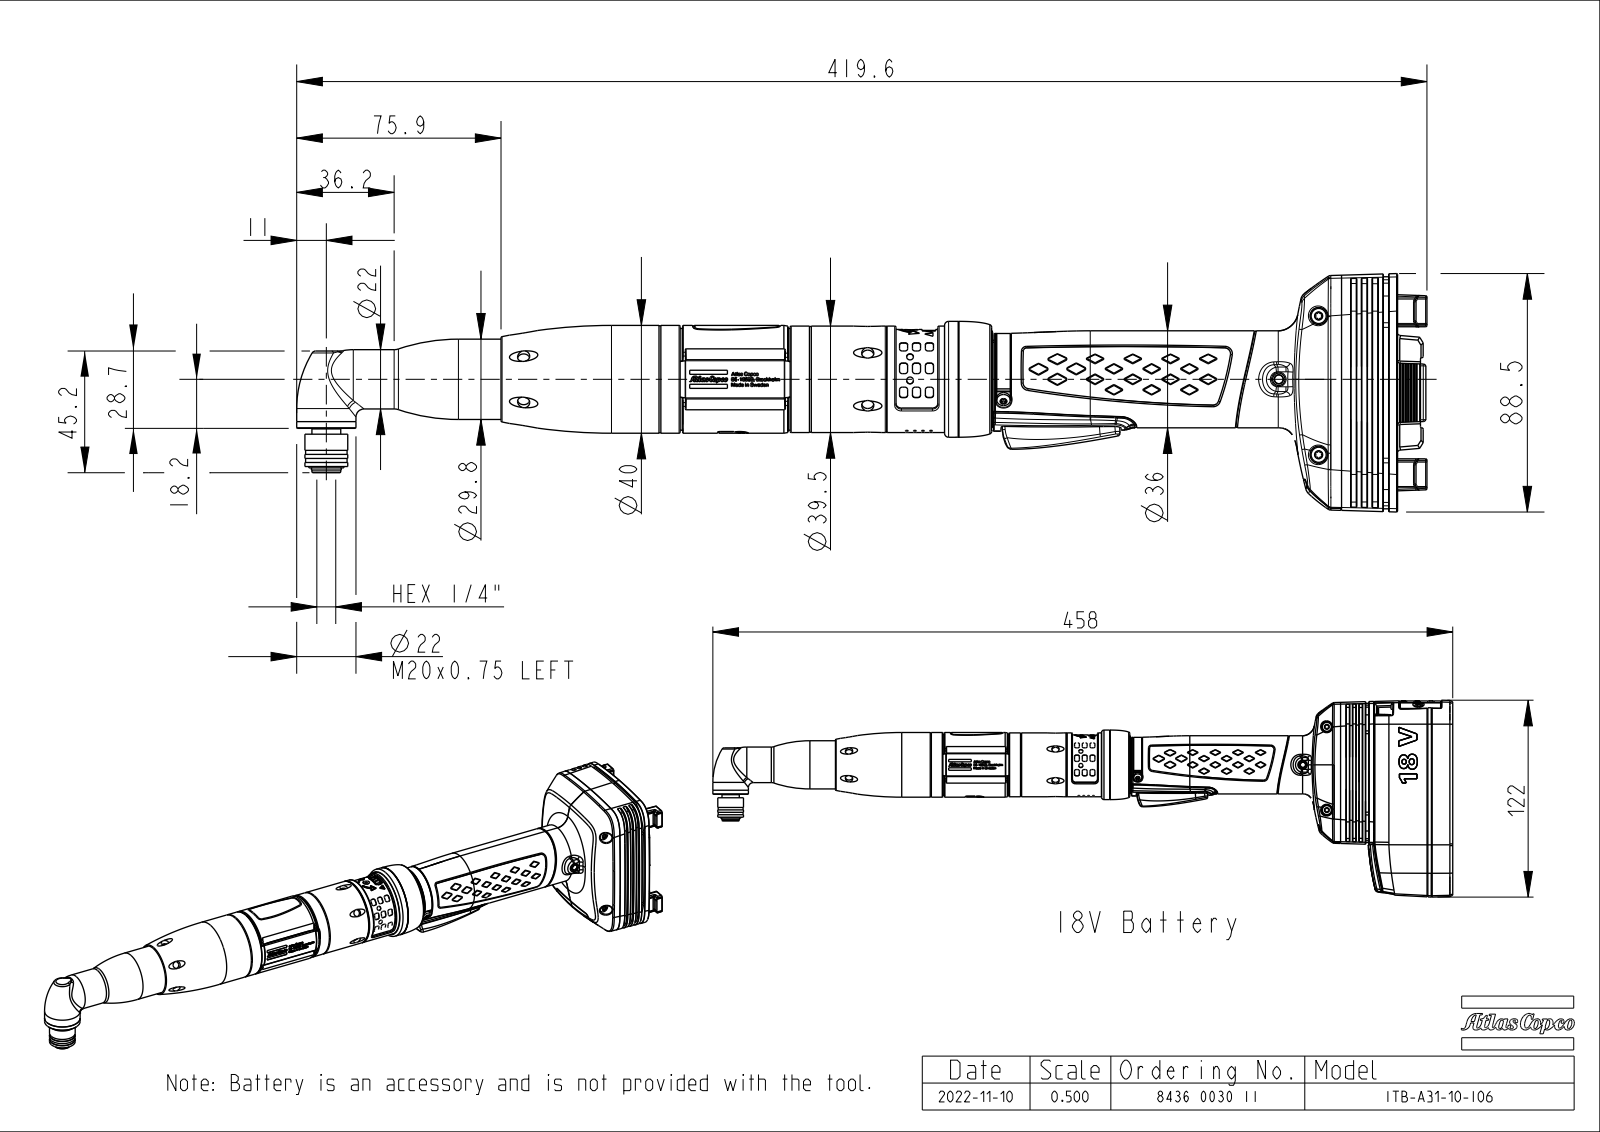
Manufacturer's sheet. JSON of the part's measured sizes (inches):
{"part_name": "PRT0023; MSBR-3_1_2; MSBR-2_1_2; MSBR-1_1_2 (+5 more)", "step_written_by": "CREO PARAMETRIC BY PTC INC, 2020281 (CONFIG_CONTROL_DESIGN)", "units": "inches", "bodies": {"solids": 6, "faces": 5012, "planar": 2024, "cylindrical": 1072, "other": 1916}, "overall_size": [16.522, 3.484, 2.935], "volume_in3": 37.04, "surface_area_in2": 132.8, "round_holes": [[0.039, 12], [0.177, 6], [0.102, 4], [0.063, 2], [0.079, 2], [0.197, 2], [0.472, 2], [0.126, 1], [0.128, 1], [0.138, 1], [0.186, 1], [0.244, 1]], "round_bosses_or_shafts": [[0.866, 2], [0.22, 2], [1.693, 1], [1.575, 1], [1.555, 1], [1.476, 1], [1.425, 1], [1.417, 1]], "partial_cylinders_radius": [[0.02, 117], [0.039, 66], [0.008, 37], [0.079, 26], [0.012, 25], [0.009, 18], [0.016, 18], [0.011, 12]], "face_to_face_distances": [0.079, 0.236, 0.157, 8.878, 0.138, 8.74, 0.315, 0.413, 9.154, 9.291], "hole_center_spacings": [0.118, 0.236, 0.346, 0.49, 0.354, 5.032, 0.693, 2.905]}
